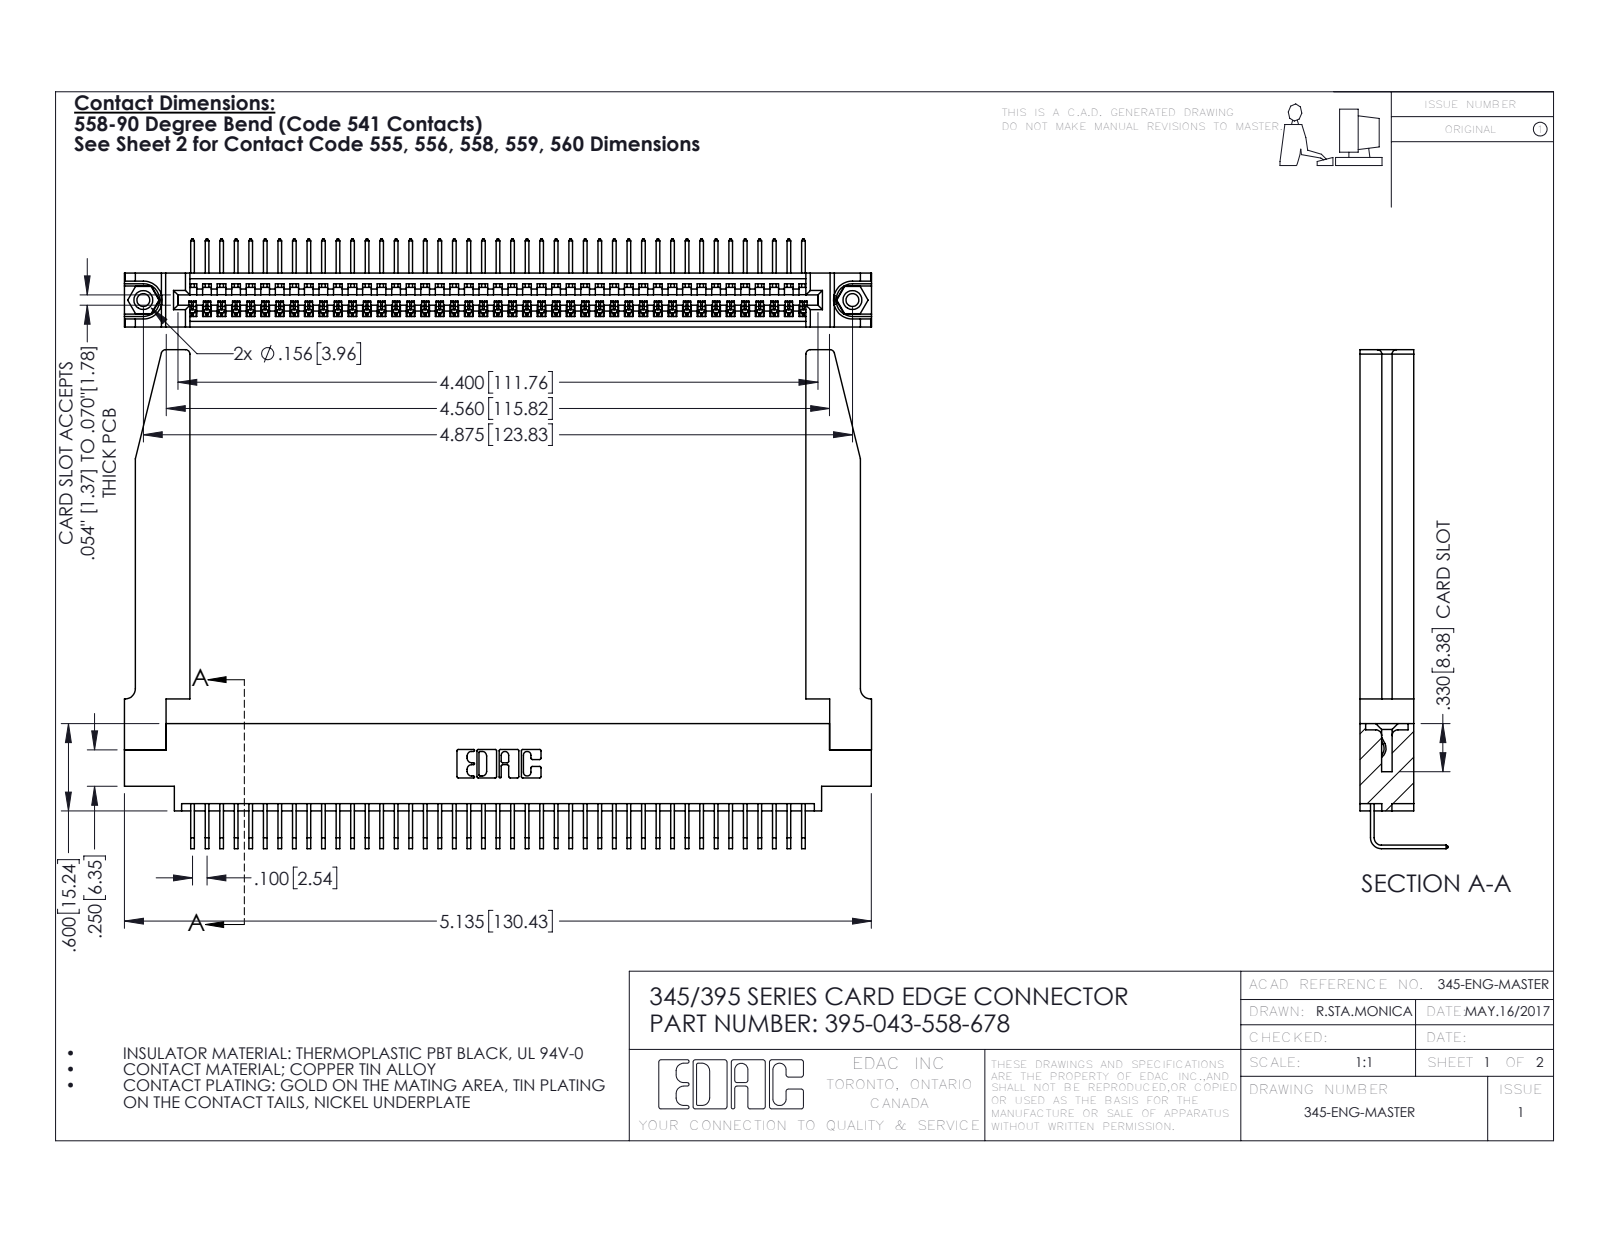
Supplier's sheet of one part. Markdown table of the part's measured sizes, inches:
| quantity | value |
| --- | --- |
| part name | 345-250-001_345-250-001-102; 345-220-078_345-220-078; 395-043-558-678; 345 Part_0.170 Offset - 0.156 Dia-TH (+1 more) |
| STEP written by | SolidWorks 2016 (CONFIG_CONTROL_DESIGN) |
| units | inches |
| bodies | 48 solids, 2944 faces (2032 planar, 860 cylindrical, 52 other) |
| overall size | 5.136 × 3.429 × 0.605 |
| volume | 1.233 in³ |
| surface area | 37.73 in² |
| round holes (diameter × count) | 0.089 × 2, 0.125 × 2, 0.156 × 2, 0.064 × 1 |
| round bosses / shafts (diameter × count) | 0.155 × 2 |
| partial cylindrical surfaces (radius × count) | 0.006 × 86, 0.01 × 22, 0.03 × 8, 0.007 × 6, 0.031 × 6, 0.026 × 3, 0.031 × 2, 0.04 × 2 |
| main face-to-face distances | 0.37, 0.072, 0.298, 0.098, 0.272, 0.025, 0.2, 0.225, 0.148, 0.15 |
| hole center spacings | 0.27, 4.639, 4.875 |
